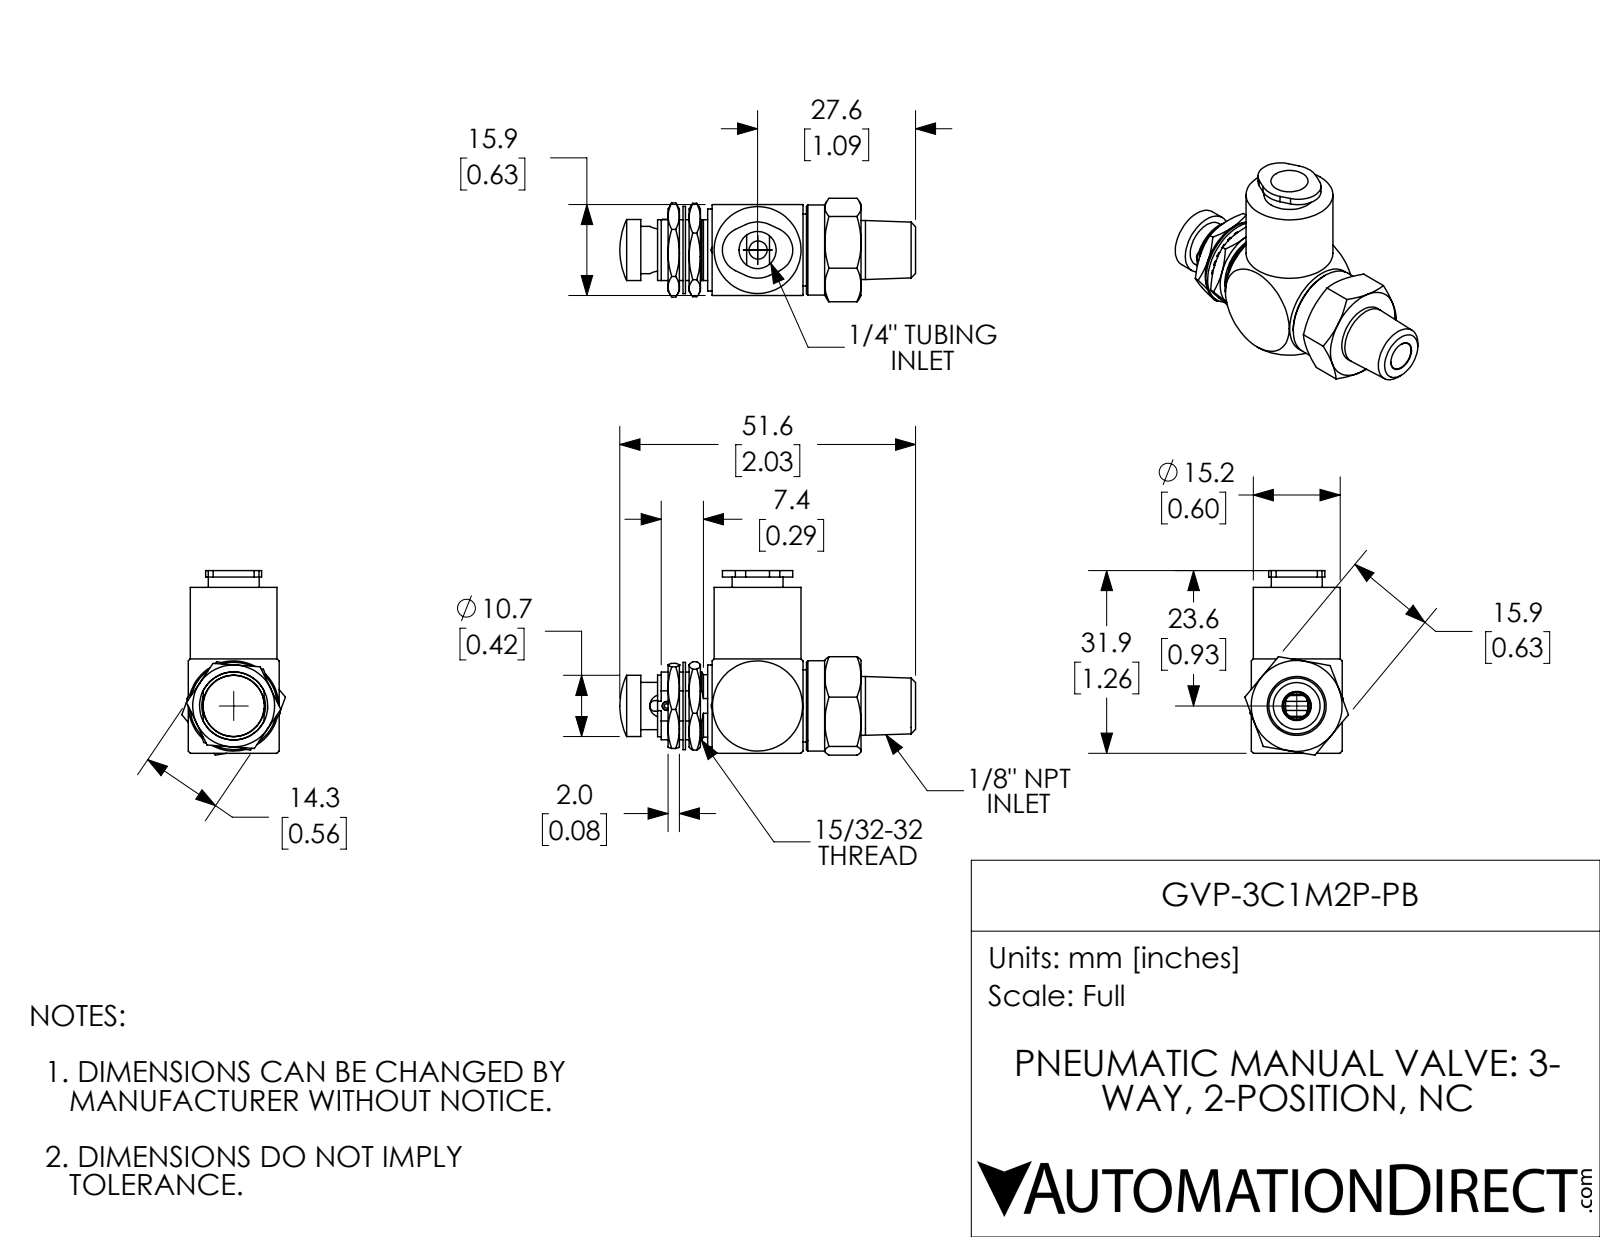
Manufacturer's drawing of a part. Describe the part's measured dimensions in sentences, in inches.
The part is named "GVP-3C1M2P-PB". Its 3-D file was written by "SolidWorks 2018 (AUTOMOTIVE_DESIGN)". It is 8 solids with 350 faces: 129 planar, 149 cylindrical and 72 other. Overall it measures 2.033 by 1.268 by 0.711 inches. Its volume is 0.496 cubic inches and its surface area 13.17 square inches. Round holes: 3 of diameter 0.063, 2 of diameter 0.125, 1 of diameter 0.03, 1 of diameter 0.153, 1 of diameter 0.182, 1 of diameter 0.195, 1 of diameter 0.249, 1 of diameter 0.255, 1 of diameter 0.34, 1 of diameter 0.377, 1 of diameter 0.438, 1 of diameter 0.468. Round bosses or shafts: 1 of diameter 0.62, 1 of diameter 0.6, 1 of diameter 0.597, 1 of diameter 0.563, 1 of diameter 0.495, 1 of diameter 0.445, 1 of diameter 0.43, 1 of diameter 0.423. Partial cylindrical surfaces (rounded edges, fillets, slot ends): 2 of radius 0.037, 2 of radius 0.156, 1 of radius 0.193, 1 of radius 0.233, 1 of radius 0.239, 1 of radius 0.26. The main face-to-face distances are 0.625, 0.072, 1.14, 0.095, 0.332, 0.304, 0.128, 0.267, 0.025, 0.042. The hole center spacings are 0.291, 0.039, 0.288, 0.338, 0.377, 0.629, 0.669.
